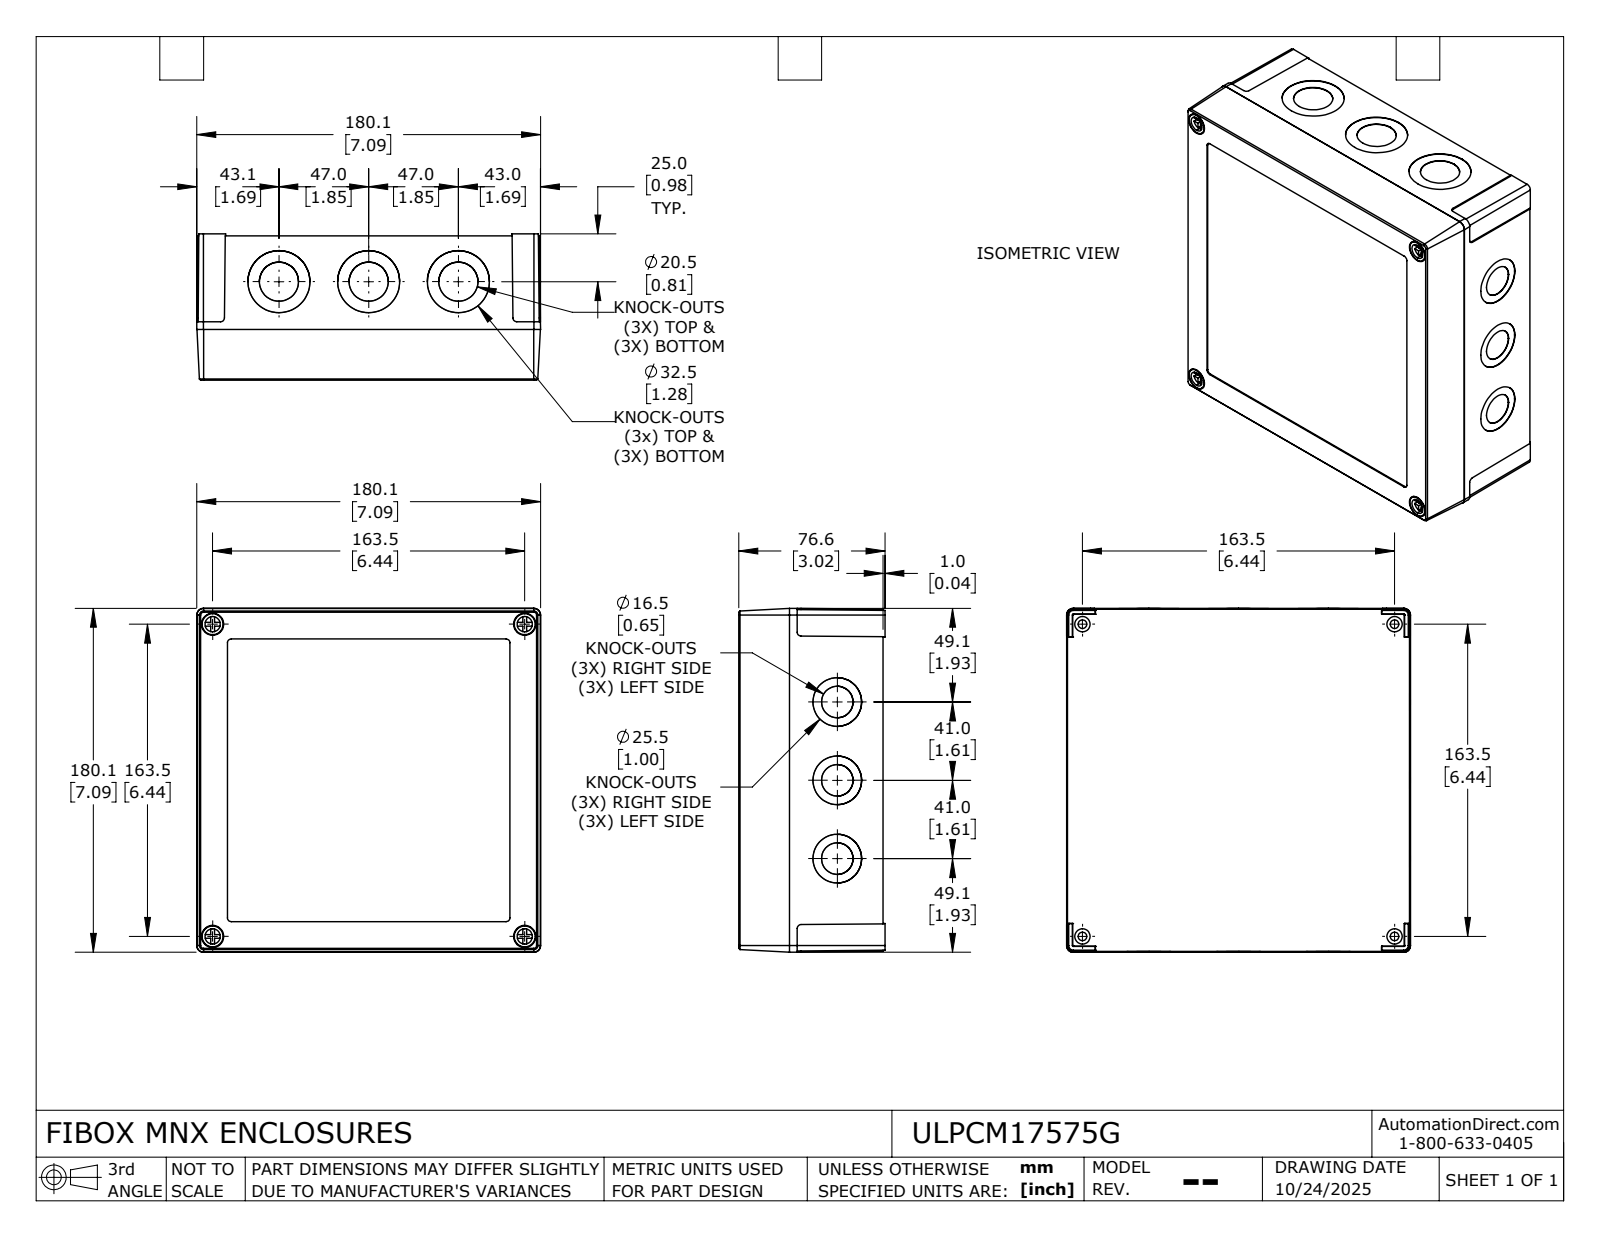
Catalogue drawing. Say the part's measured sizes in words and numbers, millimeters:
The part is named "ULPCM17575G_Default". Its 3-D file was written by "SolidWorks 2024 (CONFIG_CONTROL_DESIGN)". It is 6 solids with 582 faces: 318 planar, 224 cylindrical and 40 other. Overall it measures 180.1 by 180.1 by 76.6 millimeters. Its volume is 395 400 cubic millimeters and its surface area 246 100 square millimeters. Round holes: 12 of diameter 3.2, 12 of diameter 4, 6 of diameter 16.5, 6 of diameter 20.5, 6 of diameter 25.5, 6 of diameter 32.5, 4 of diameter 4.5, 4 of diameter 8, 4 of diameter 11.6. Round bosses or shafts: 12 of diameter 8, 8 of diameter 2.5, 4 of diameter 11, 4 of diameter 7.2. Partial cylindrical surfaces (rounded edges, fillets, slot ends): 8 of radius 2, 6 of radius 2.8, 4 of radius 1.1, 4 of radius 5, 2 of radius 1.2. The main face-to-face distances are 72.6, 3, 69.6, 4.2, 2.5, 75.1, 72.1, 75.6, 0.5, 46. The hole center spacings are 33.9, 50, 72.8, 82.6, 121.7, 132.3, 138.9, 148.7.
